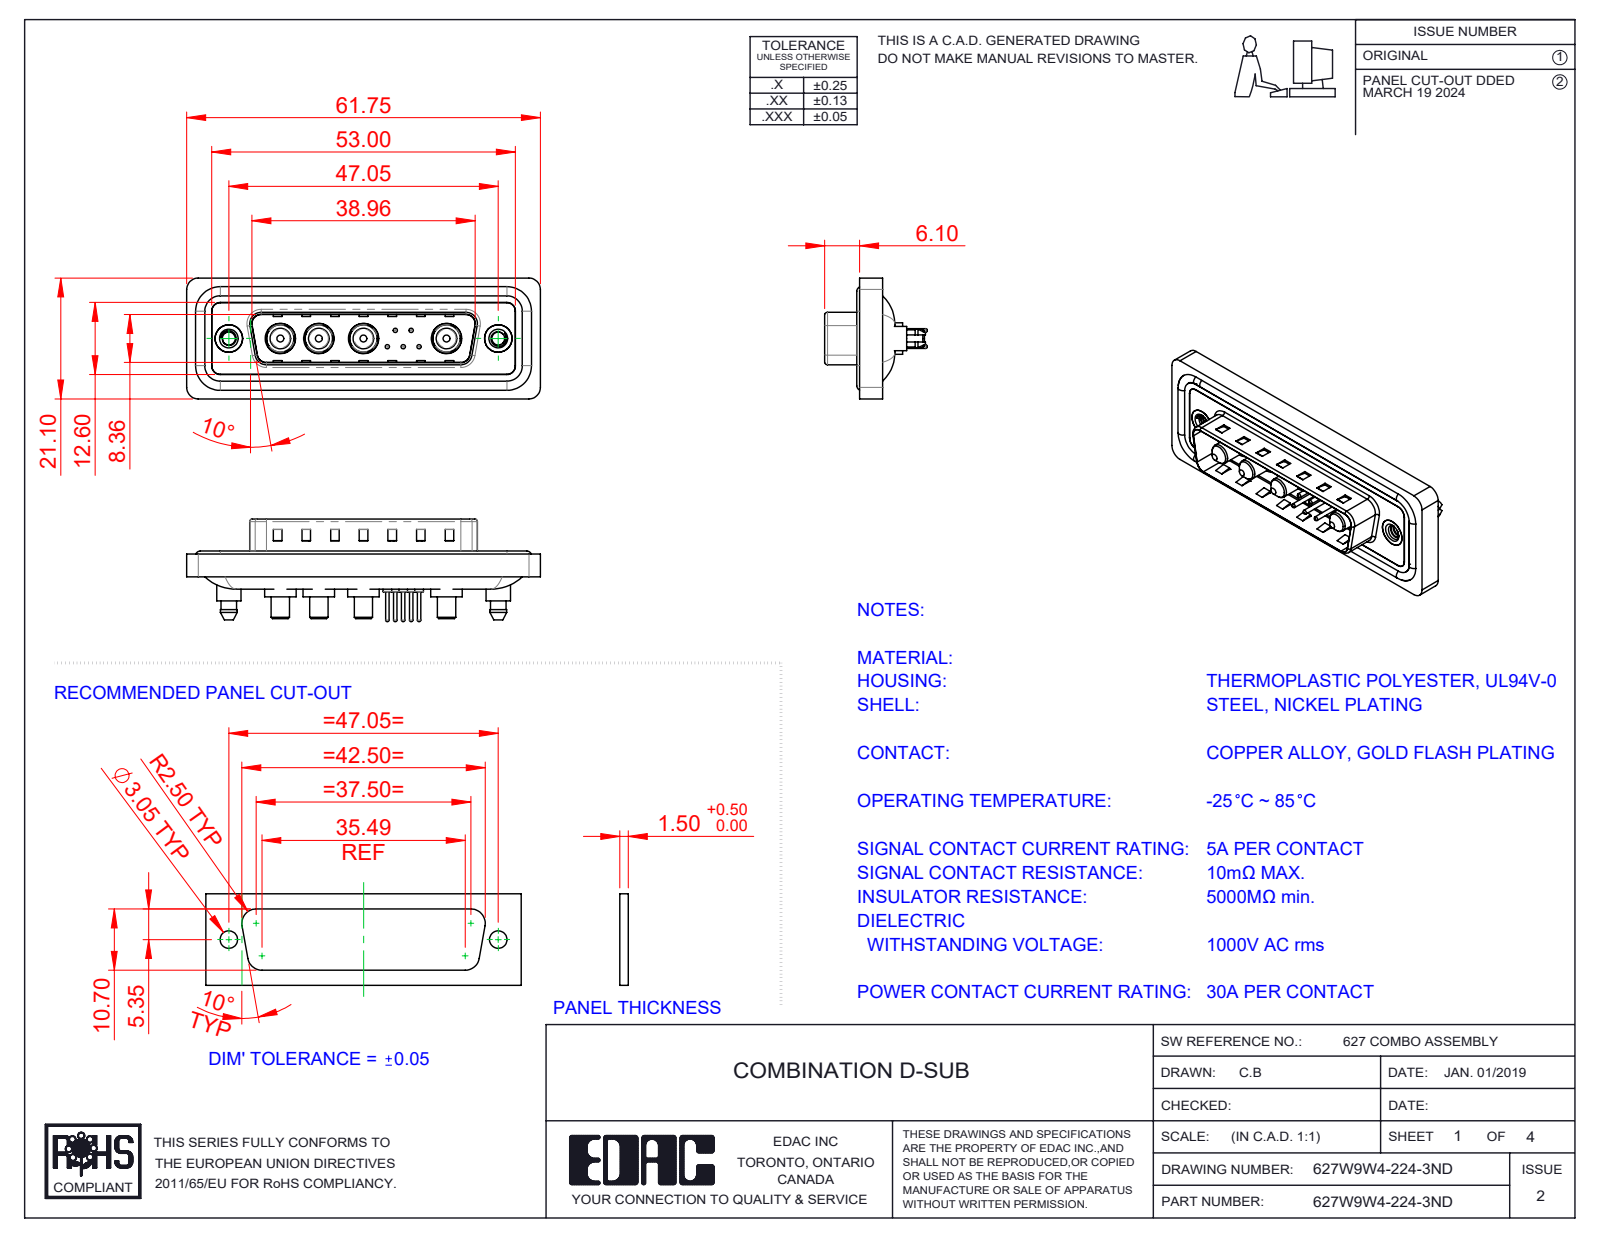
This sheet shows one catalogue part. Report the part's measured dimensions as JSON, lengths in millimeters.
{"part_name": "627Combo Threaded Boardlock_5; 627Combo Shell Rear_25 Contacts; 627W9W4-224-3ND; 627Combo Contact Row 1_24 (+6 more)", "step_written_by": "SolidWorks 2023 (CONFIG_CONTROL_DESIGN)", "units": "millimeters", "bodies": {"solids": 20, "faces": 882, "planar": 300, "cylindrical": 374, "other": 208}, "overall_size": [61.75, 21.1, 17.9], "volume_mm3": 7567, "surface_area_mm2": 12190, "round_holes": [[0.75, 5], [1.6, 5], [2, 5], [4.85, 4], [5.3, 4], [2.26, 2], [4, 2], [4.8, 2], [5, 2]], "round_bosses_or_shafts": [[1.5, 5], [0.6, 5], [5.5, 4], [5.2, 4], [4.75, 4], [3.75, 4], [3.6, 4], [3.2, 4]], "partial_cylinders_radius": [[1.5, 24], [2, 18], [1.6, 10], [0.5, 8], [0.25, 4], [0.6, 4], [0.65, 4], [0.9, 4]], "face_to_face_distances": [0.4, 1.5, 1.1, 0.5, 3.1, 1.6, 2.9, 0.82, 9.58, 5.65], "hole_center_spacings": [3.16, 2.77, 5.04, 14.51, 2.78, 4.4, 4.41, 5]}
